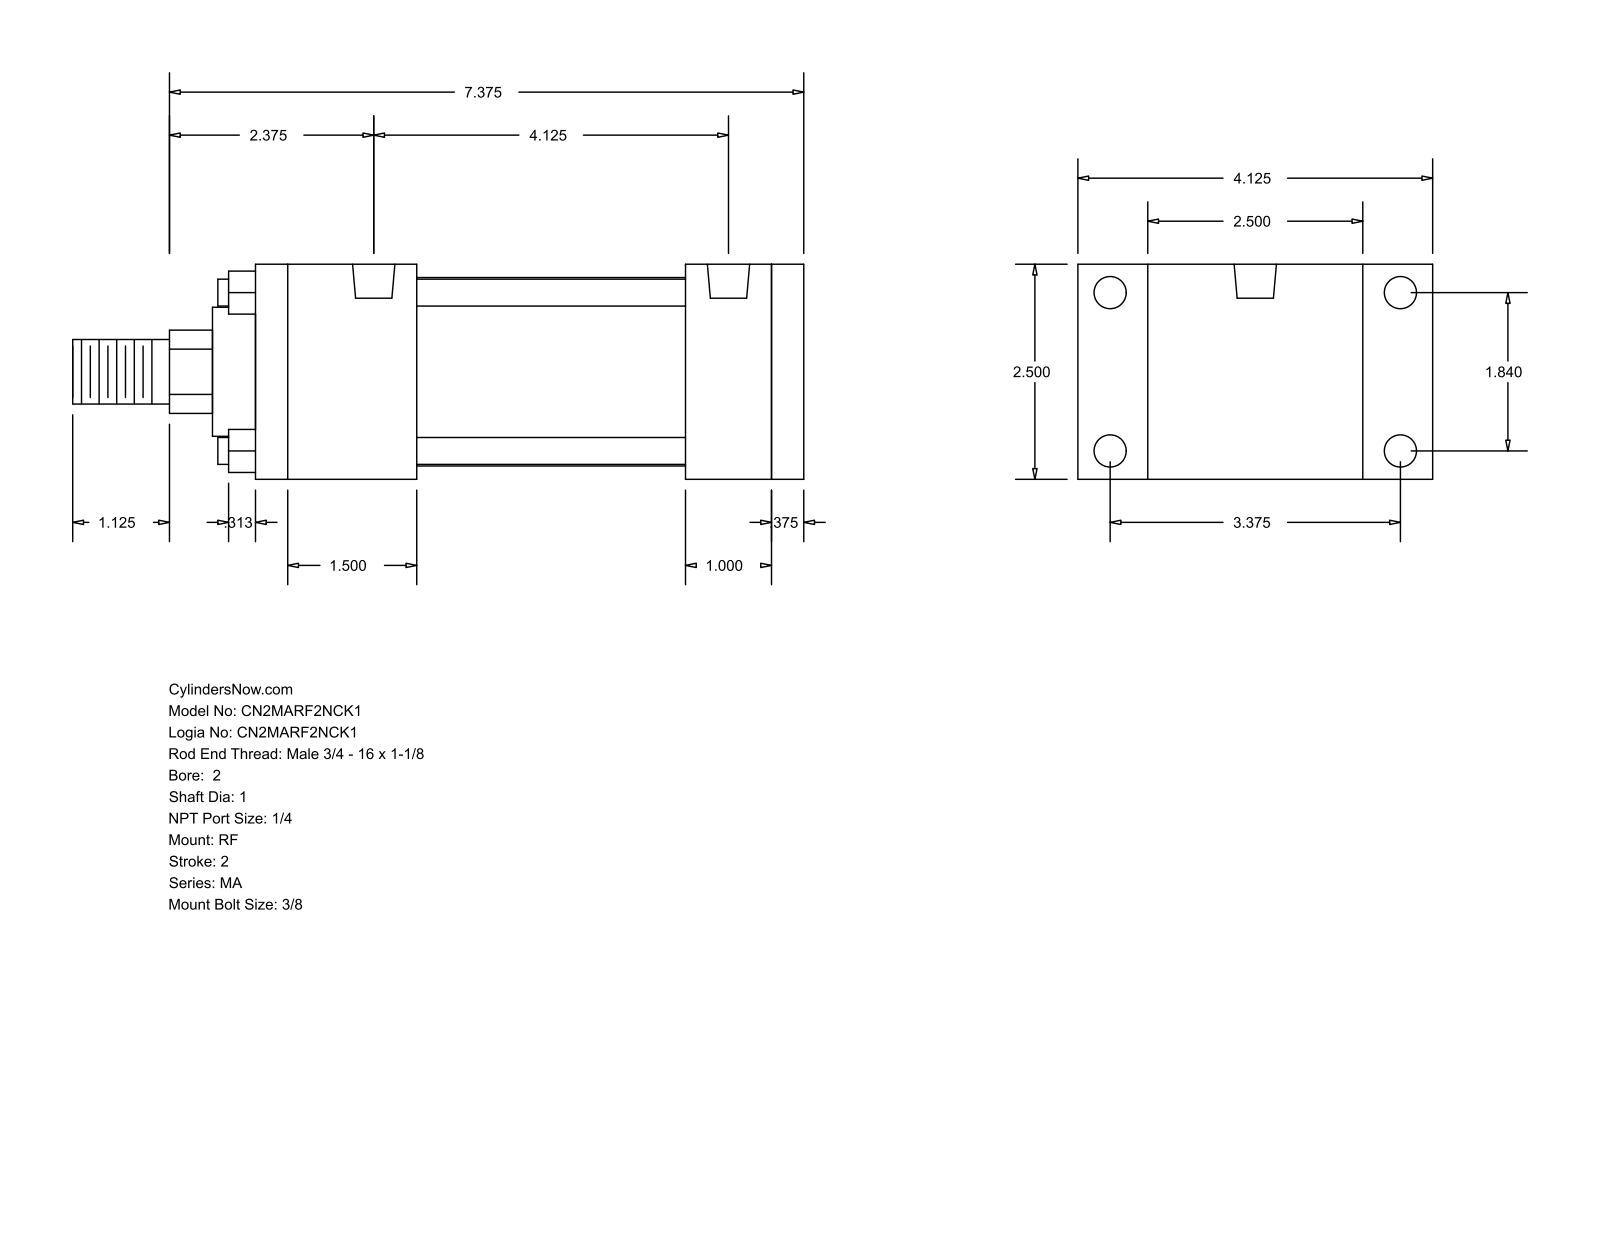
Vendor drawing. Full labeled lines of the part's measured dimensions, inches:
Part name (STEP PRODUCT): MA_RF__0200_1
STEP written by: GSSL Pune (CONFIG_CONTROL_DESIGN)
Units: inches
Bodies: 0 solids, 92 faces (64 planar, 28 cylindrical, 0 other)
Overall size (bounding box): 8.5 × 4.125 × 2.5
Round holes (diameter × count): ⌀0.313 ×4, ⌀0.375 ×4, ⌀0.492 ×2
Round bosses / shafts (diameter × count): ⌀0.313 ×4, ⌀2.19 ×1, ⌀1.5 ×1, ⌀1 ×1, ⌀0.75 ×1
Partial cylindrical surfaces — rounded edges, fillets, slot ends (radius × count): R0.484 ×1
Main face-to-face distances: 2.5, 6, 0.375, 6.375, 1, 0.813, 0.5, 1.875, 4.125, 4.5
Hole centre spacings: 1.84, 3.375, 3.844, 4.125
